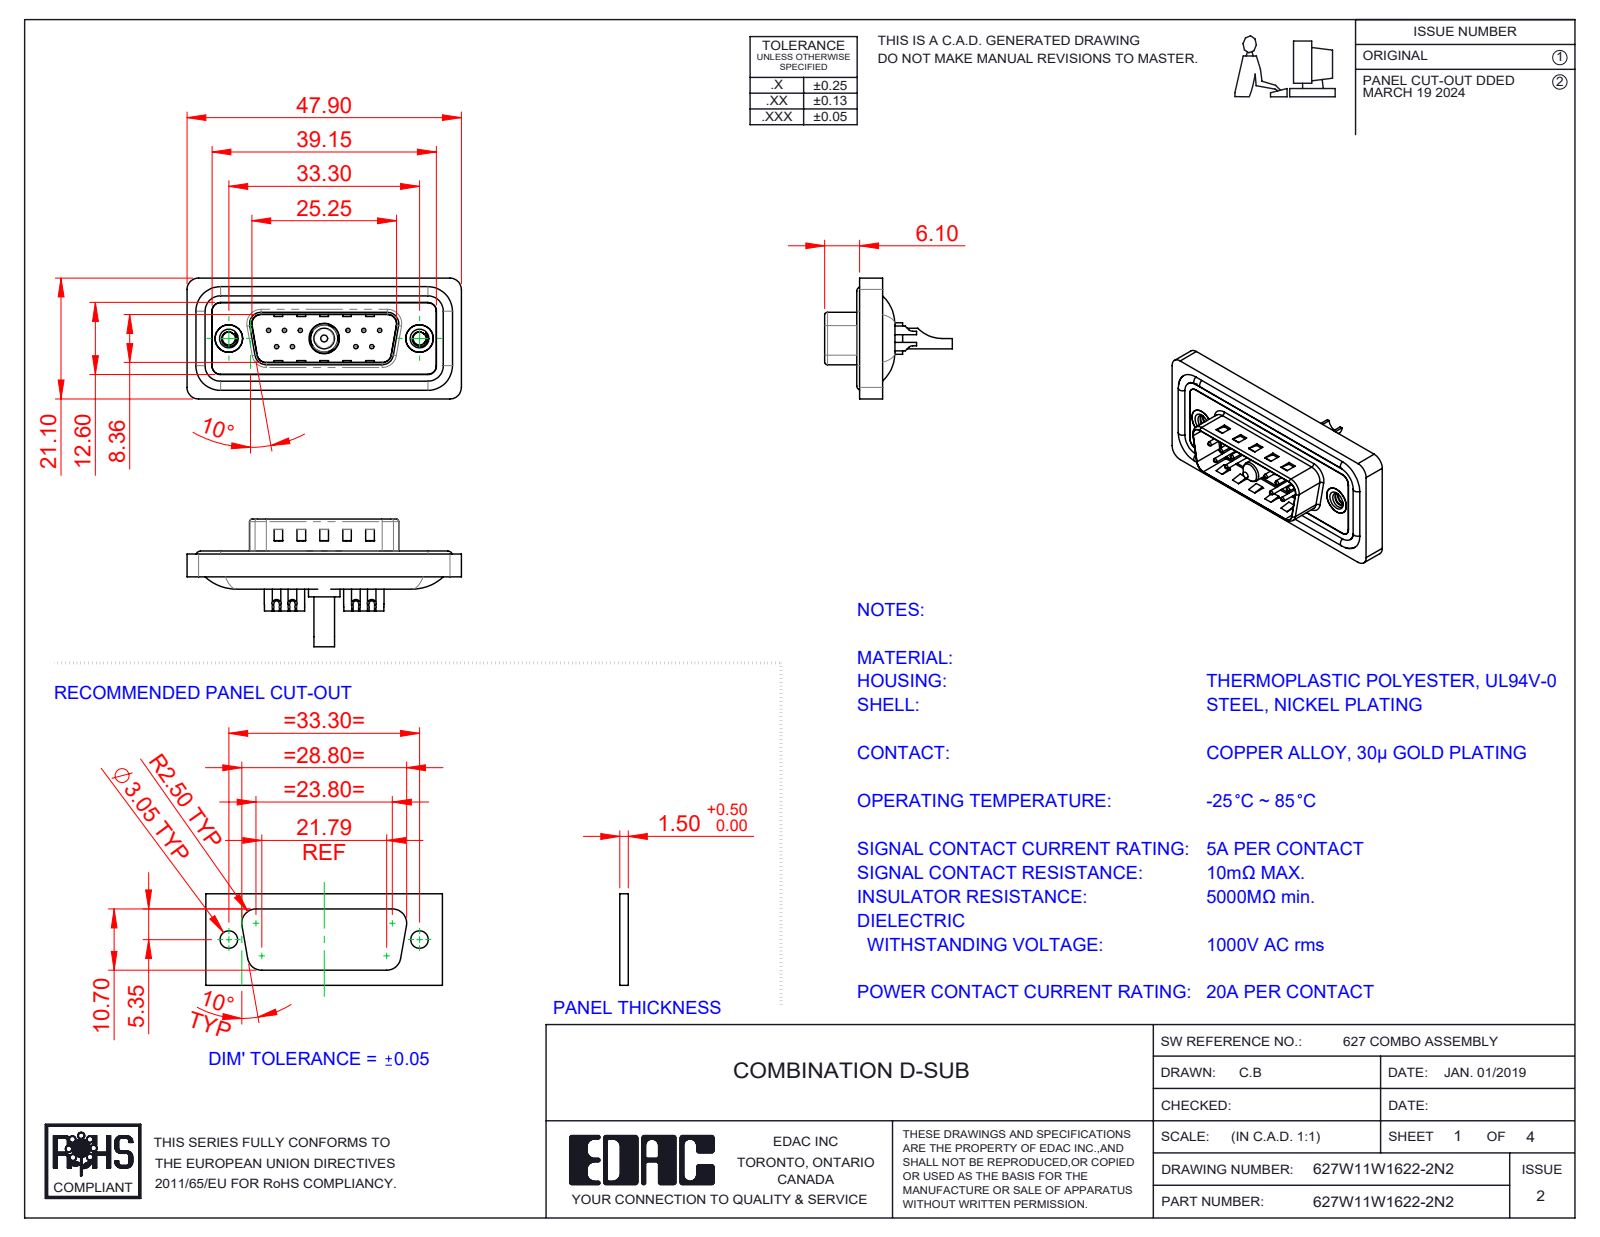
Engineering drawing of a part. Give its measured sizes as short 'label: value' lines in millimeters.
name: 627Combo Shell Rear_15 Contacts; Power Pin_20A SC; 627Combo Waterproof Housing_15 Contacts; 627Combo Housing_11W1 (+5 more)
written by: SolidWorks 2023 (CONFIG_CONTROL_DESIGN)
unit: mm
bodies: 19 solids, 876 faces (289 planar, 370 cylindrical, 217 other)
size: 47.9 × 22.3 × 21.1
volume: 5 476 mm³; area: 8 998 mm²
holes: 10× ⌀0.75, 10× ⌀1, 10× ⌀1.6, 10× ⌀2, 2× ⌀2.26, 2× ⌀4, 2× ⌀4.8, 2× ⌀5, 1× ⌀2.7, 1× ⌀4.85, 1× ⌀5.3
bosses: 10× ⌀1.5, 4× ⌀1.6, 2× ⌀4.9, 1× ⌀5.5, 1× ⌀5.2, 1× ⌀4.75, 1× ⌀3.75, 1× ⌀3.6
rounds: 26× R1.5, 20× R2, 9× R1, 8× R0.5, 8× R1.6, 4× R0.25, 4× R0.6, 4× R0.65
face distances: 0.4, 1.1, 1.6, 1.5, 0.5, 2.9, 3.1, 2.5, 4.1, 0.82
hole spacings: 3.16, 2.77, 13.85, 11.08, 16.62, 5.03, 5.04, 5.54
